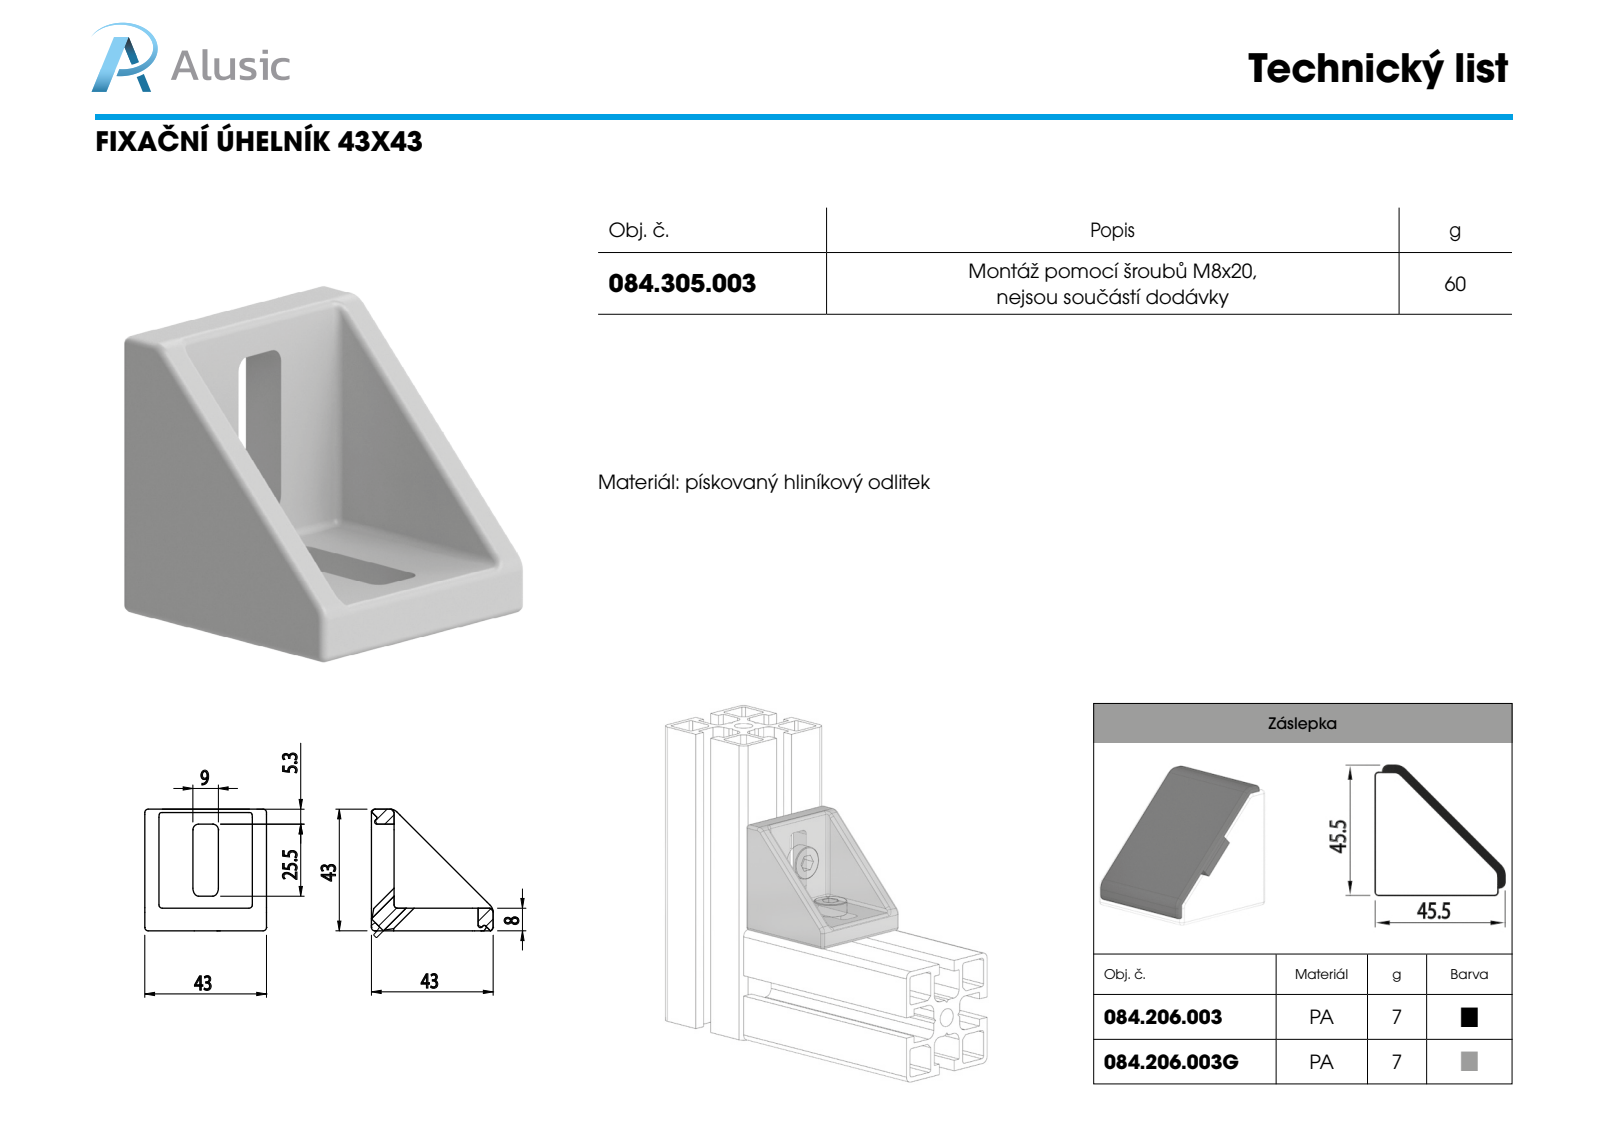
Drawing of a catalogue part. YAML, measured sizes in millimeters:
part_name: "084.305.003"
step_written_by: "SolidWorks 2018 (CONFIG_CONTROL_DESIGN)"
units: millimeters
bodies: {solids: 1, faces: 260, planar: 47, cylindrical: 101, other: 112}
overall_size: [43, 43, 43]
volume: 22948
surface_area: 11353
partial_cylinders:
  - {radius: 2, count: 24}
  - {radius: 1.2, count: 22}
  - {radius: 0.8, count: 14}
  - {radius: 1.5, count: 12}
  - {radius: 0.5, count: 10}
  - {radius: 1, count: 2}
  - {radius: 3.5, count: 2}
face_to_face_distances: [43, 38, 4.5, 5, 12, 17, 26, 21, 9, 3.5]
